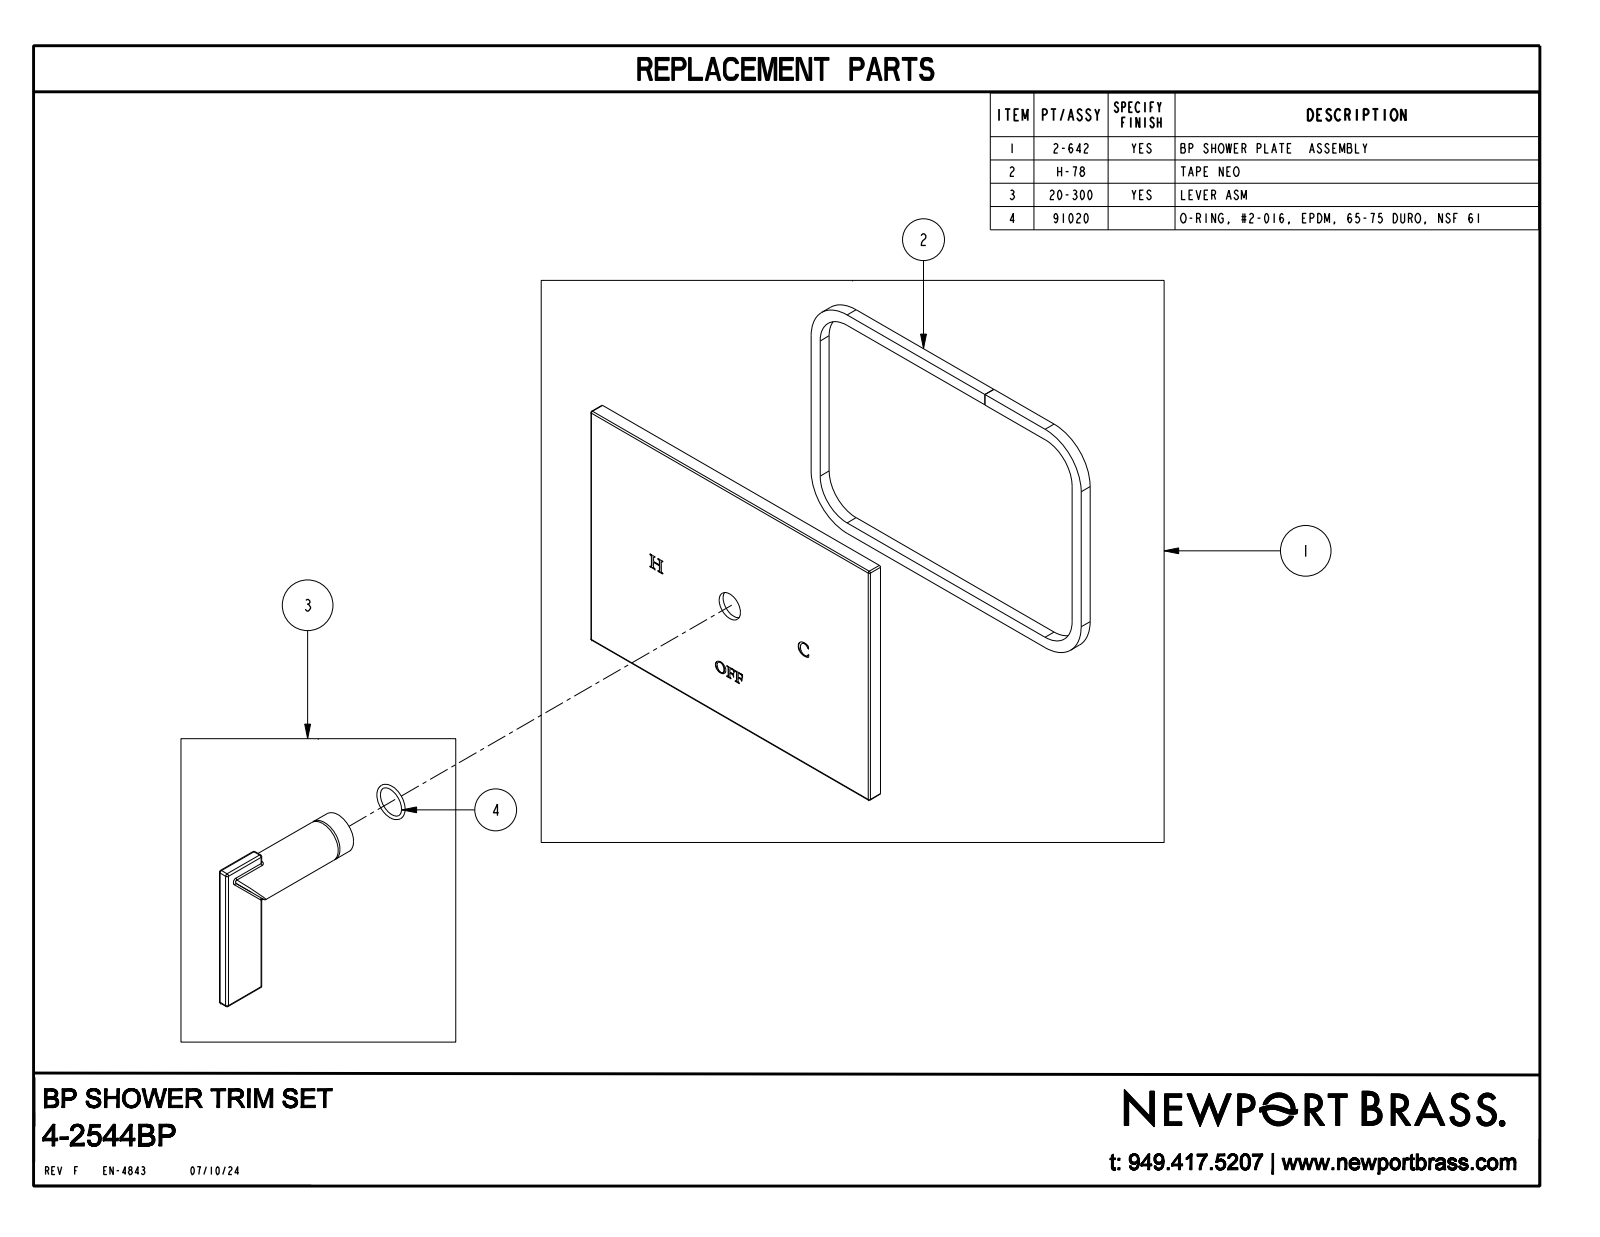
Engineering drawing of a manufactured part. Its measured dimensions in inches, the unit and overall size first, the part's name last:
Units: inches
Overall size (bounding box): 7.75 × 5.5 × 3.51
Round bosses / shafts (diameter × count): ⌀0.86 ×1, ⌀0.68 ×1
Partial cylindrical surfaces — rounded edges, fillets, slot ends (radius × count): R0.04 ×16, R0.03 ×8
Main face-to-face distances: 0.31, 3.757, 3.993, 0.236, 5.5, 7.75, 3.51, 3.2, 2.526, 2.216
Volume: 15.38 in³ · Surface area: 107.5 in²
Bodies: 1 solid, 293 faces (57 planar, 32 cylindrical, 204 other)
Part name (STEP PRODUCT): 4-2544BP
STEP written by: CREO PARAMETRIC BY PTC INC, 2018400 (CONFIG_CONTROL_DESIGN)
